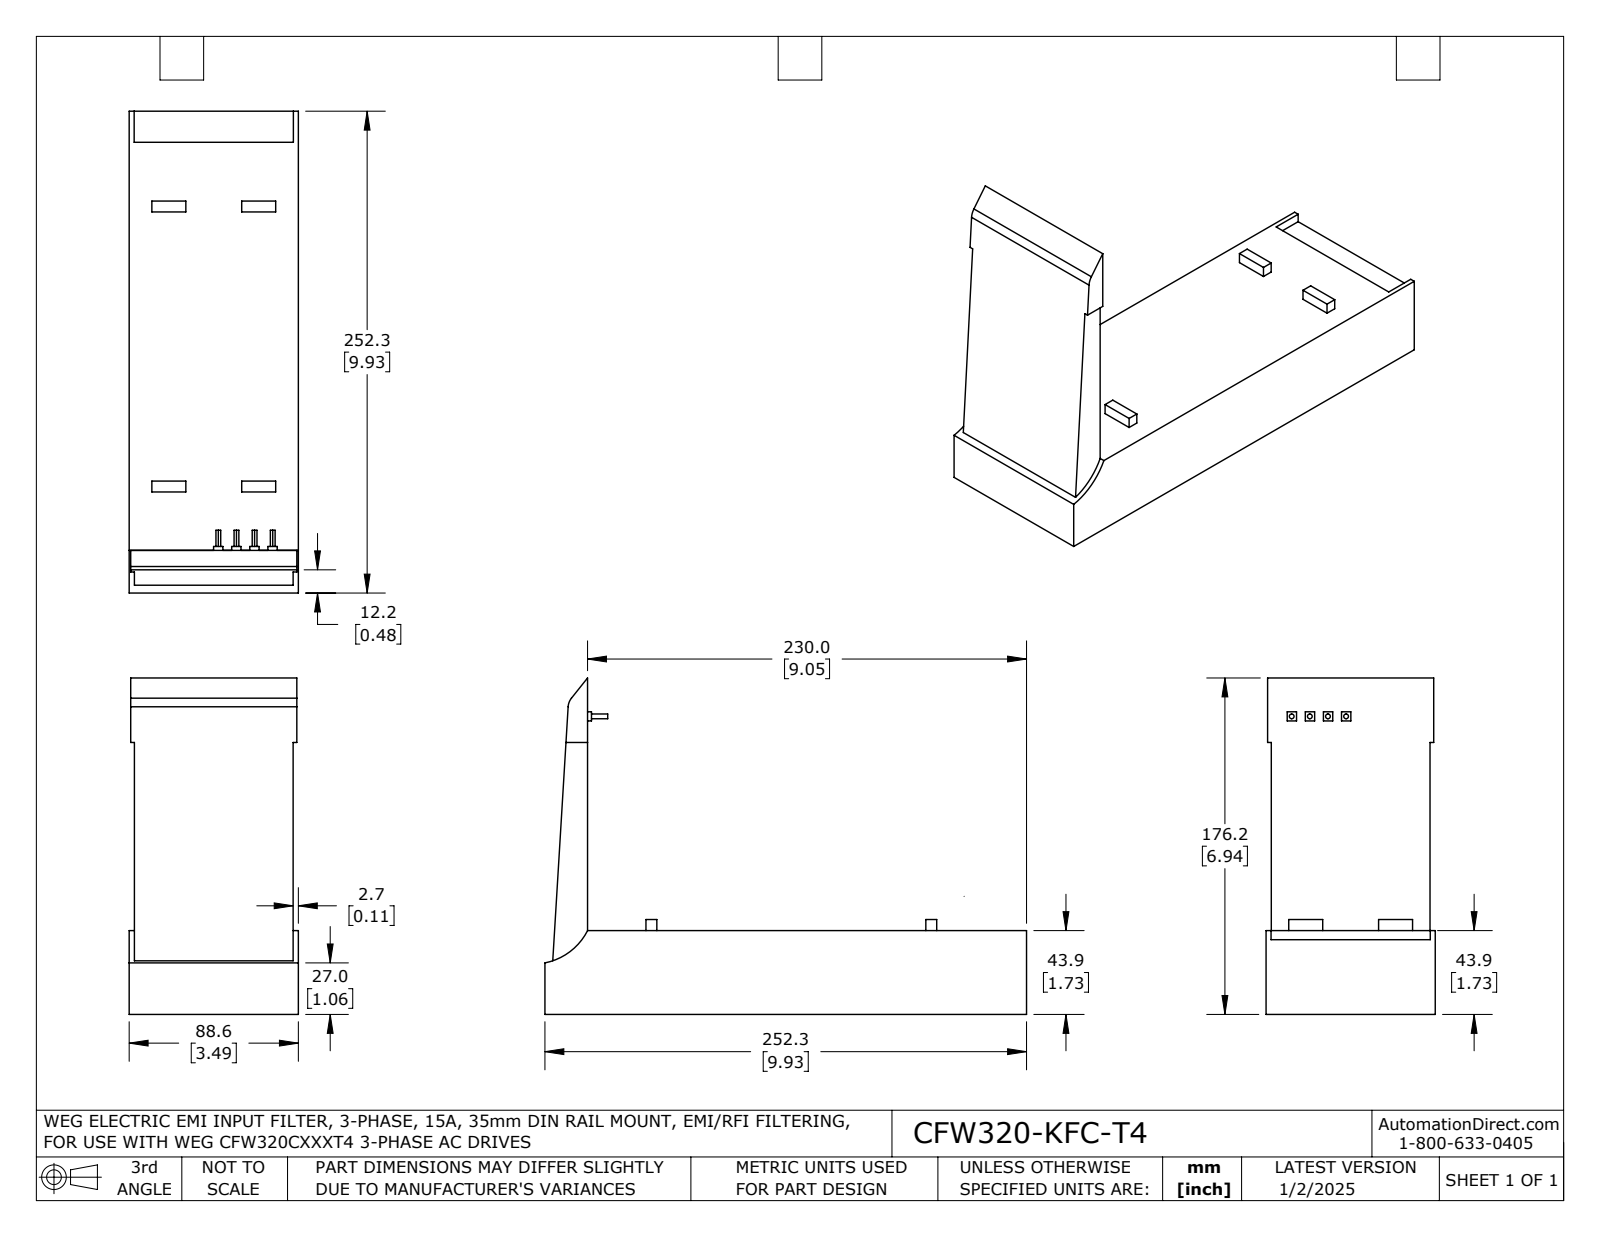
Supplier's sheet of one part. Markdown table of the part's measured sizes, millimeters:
| quantity | value |
| --- | --- |
| part name | CFW320-KFC-T4 |
| STEP written by | SolidWorks 2021 (AUTOMOTIVE_DESIGN) |
| units | millimeters |
| bodies | 1 solid, 73 faces (63 planar, 10 cylindrical, 0 other) |
| overall size | 252.3 × 176.2 × 88.6 |
| volume | 1 112 000 mm³ |
| surface area | 100 500 mm² |
| round bosses / shafts (diameter × count) | 2.5 × 4 |
| partial cylindrical surfaces (radius × count) | 8 × 1, 32 × 1 |
| main face-to-face distances | 43.9, 88.6, 230, 2.7, 85.9, 252.3, 22.3, 83.2, 39.1, 4.8 |
